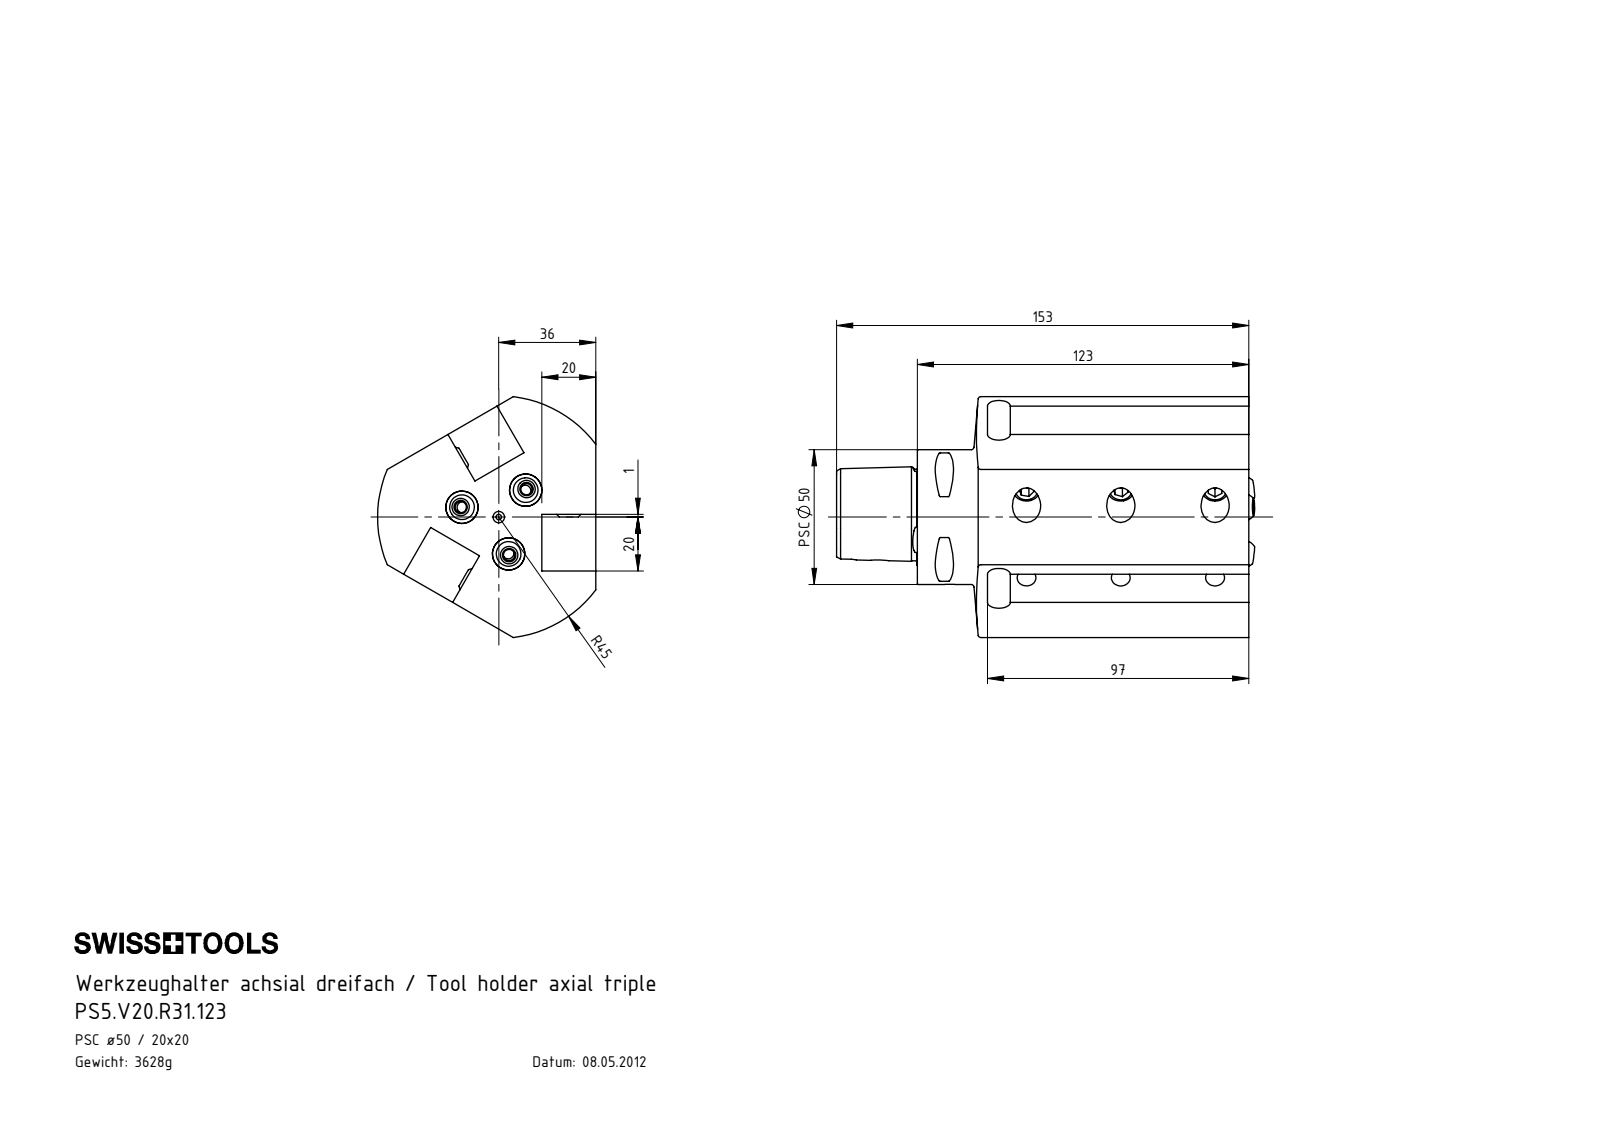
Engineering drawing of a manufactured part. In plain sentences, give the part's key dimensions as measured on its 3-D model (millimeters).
The part is named "KU1-U12.001.010_1; KU1-U12.001.010; ISO 4026 - M10 x 25; PS5-V20.R31.123_A (+2 more)". Its 3-D file was written by "SolidWorks 2017 (AUTOMOTIVE_DESIGN)". It is 16 solids with 419 faces: 127 planar, 126 cylindrical and 166 other. Overall it measures 154.8 by 89.35 by 81 millimeters. Its volume is 460 354 cubic millimeters and its surface area 83 942 square millimeters. Round holes: 10 of diameter 8.5, 9 of diameter 11, 6 of diameter 4.2, 3 of diameter 7, 3 of diameter 12, 1 of diameter 2, 1 of diameter 4, 1 of diameter 6.1, 1 of diameter 14.5, 1 of diameter 21, 1 of diameter 24. Round bosses or shafts: 9 of diameter 10, 1 of diameter 50. Partial cylindrical surfaces (rounded edges, fillets, slot ends): 8 of radius 0.5, 6 of radius 5, 1 of radius 4, 1 of radius 45. The main face-to-face distances are 20, 21, 97, 123, 26, 115, 89, 8, 5, 30. The hole center spacings are 35, 14.14, 24.49, 70, 26, 38.58, 60.38, 68.62.
